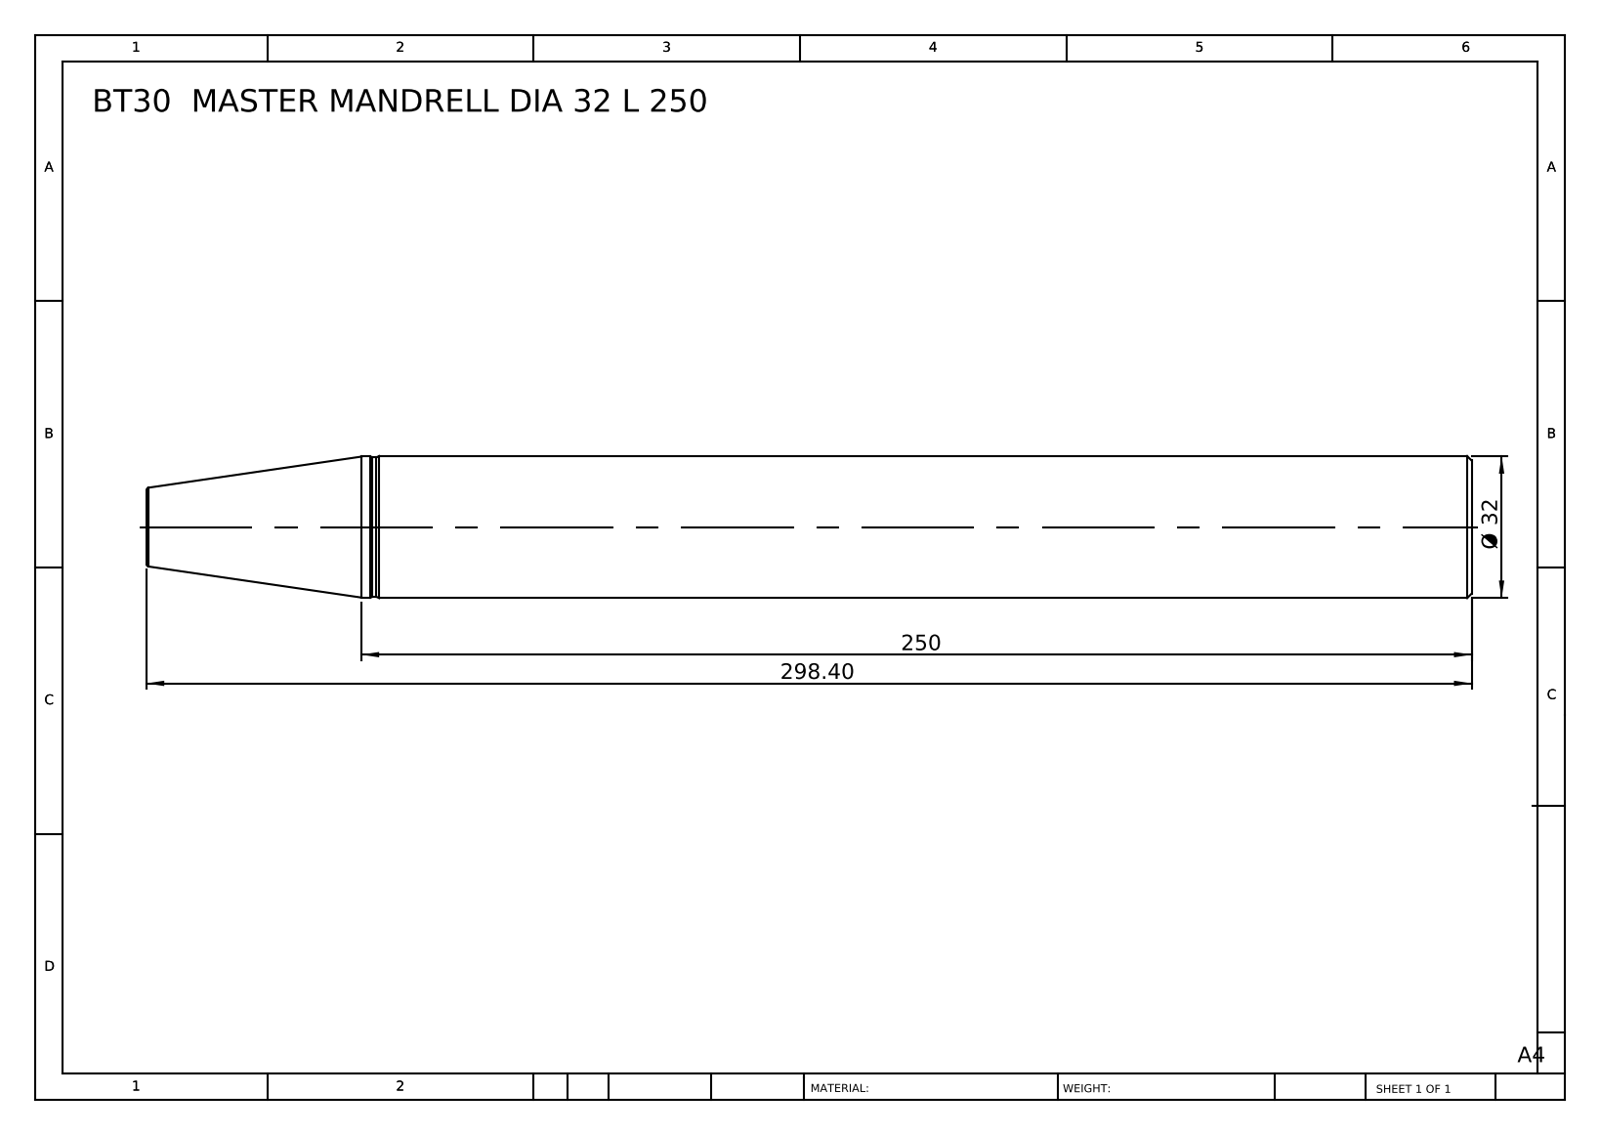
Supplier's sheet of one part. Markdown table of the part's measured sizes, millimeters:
| quantity | value |
| --- | --- |
| part name | BT30 MASTER MANDRELL DIA 32 L 250 |
| STEP written by | SolidWorks 2014 (CONFIG_CONTROL_DESIGN) |
| units | millimeters |
| bodies | 1 solid, 18 faces (2 planar, 6 cylindrical, 10 other) |
| overall size | 298.4 × 32 × 32 |
| volume | 224 743 mm³ |
| surface area | 29 914 mm² |
| round bosses / shafts (diameter × count) | 32 × 1, 31.75 × 1, 31.35 × 1 |
| main face-to-face distances | 298.4 |
